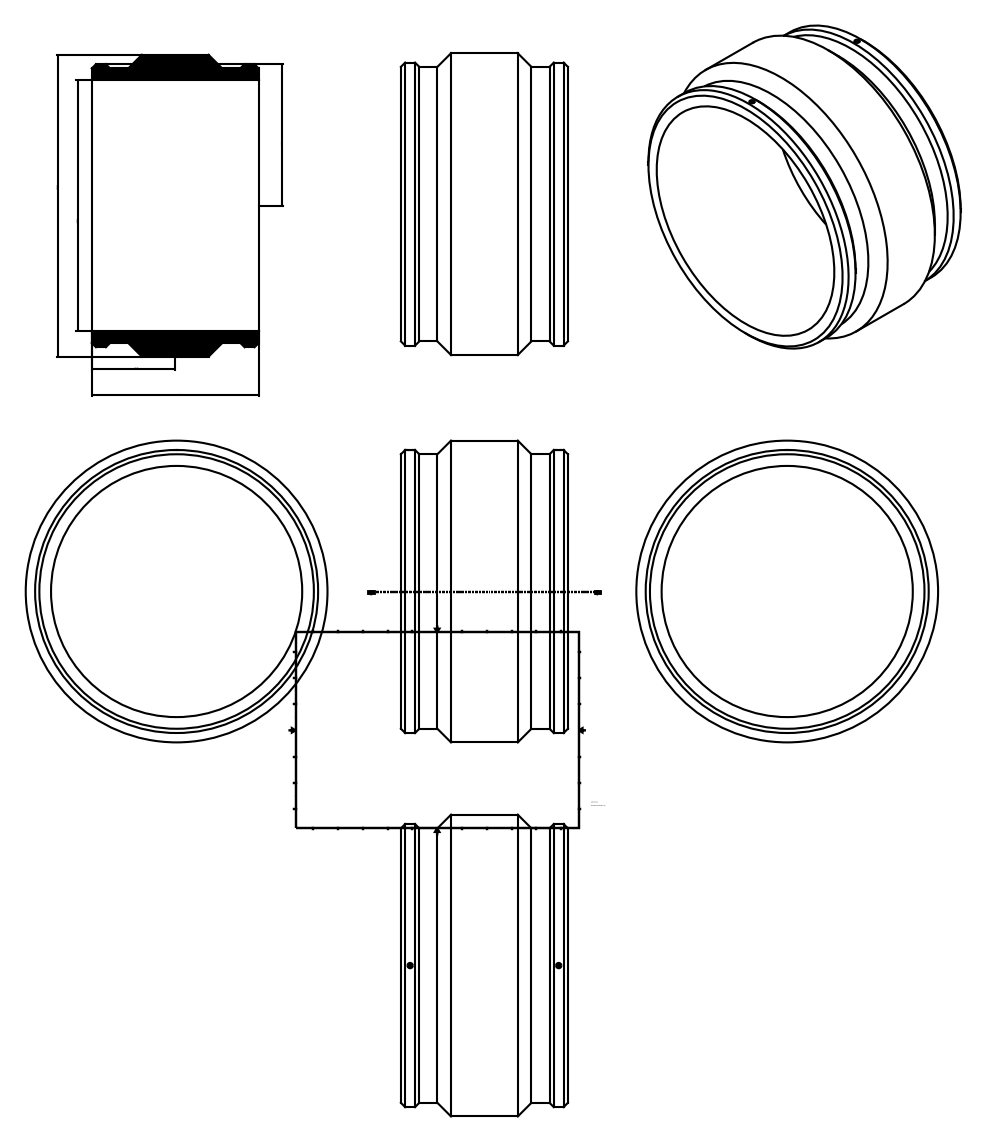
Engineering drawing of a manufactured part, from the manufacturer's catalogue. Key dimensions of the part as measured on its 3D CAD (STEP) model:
Part name (STEP PRODUCT): 490103710
STEP written by: Autodesk Inventor 2015 (AUTOMOTIVE_DESIGN)
Units: millimetres
Bodies: 1 solid, 28 faces (8 planar, 14 cylindrical, 6 other)
Overall size (bounding box): 853 × 853 × 472
Volume: 61 060 000 mm³ · Surface area: 2 551 000 mm²
Round holes (diameter × count): ⌀10 ×2, ⌀710 ×1
Round bosses / shafts (diameter × count): ⌀15 ×2, ⌀4 ×2, ⌀853 ×1, ⌀800 ×1, ⌀776 ×1
Main face-to-face distances: 472, 14, 11, 3
Hole centre spacings: 420.08
